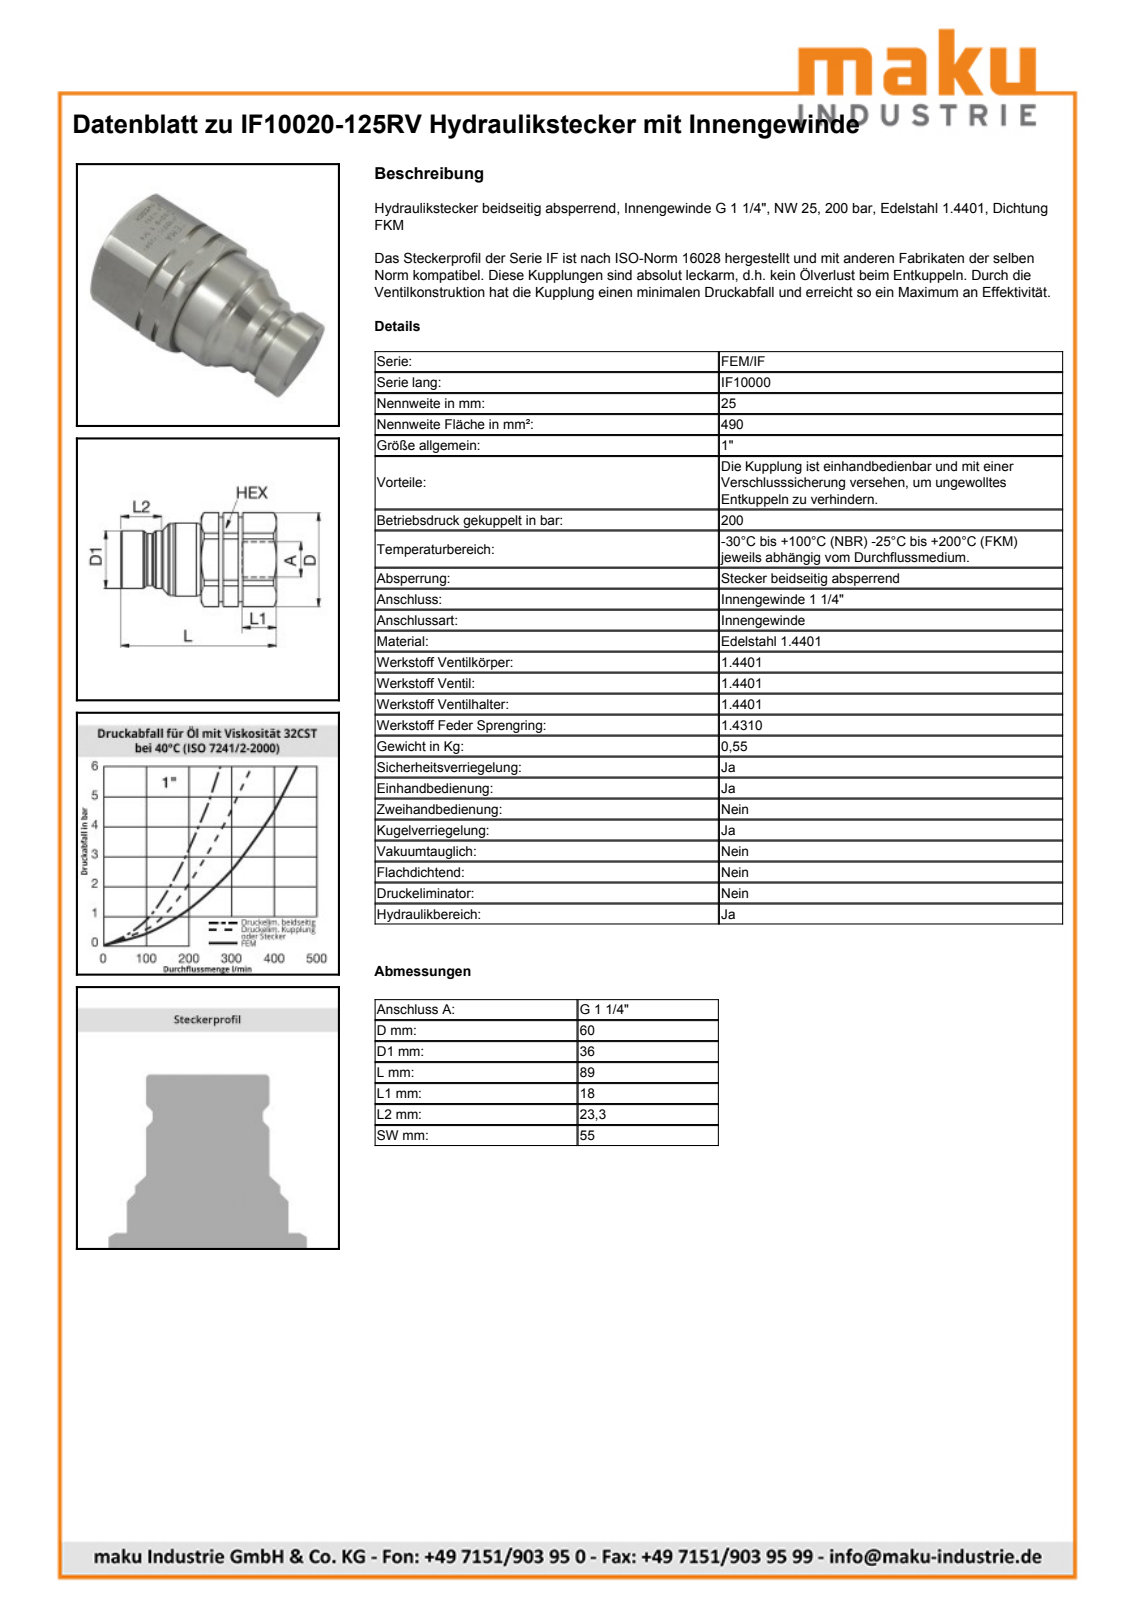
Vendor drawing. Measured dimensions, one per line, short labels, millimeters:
name: IF10020-125RV
written by: SolidWorks 2009 (AUTOMOTIVE_DESIGN)
unit: mm
bodies: 1 solid, 169 faces (57 planar, 58 cylindrical, 54 other)
size: 92.6 × 60 × 55
volume: 144 869 mm³; area: 24 450 mm²
holes: 6× ⌀7, 1× ⌀10.2, 1× ⌀23.7, 1× ⌀29, 1× ⌀38.95
bosses: 1× ⌀55, 1× ⌀50, 1× ⌀47.81, 1× ⌀45.3, 1× ⌀36, 1× ⌀32, 1× ⌀23.48, 1× ⌀10
rounds: 1× R30
face distances: 55, 92.6, 48.6, 44, 8, 8.65, 2.15, 64.6, 16, 28
hole spacings: 11.4, 19.74, 22.8
